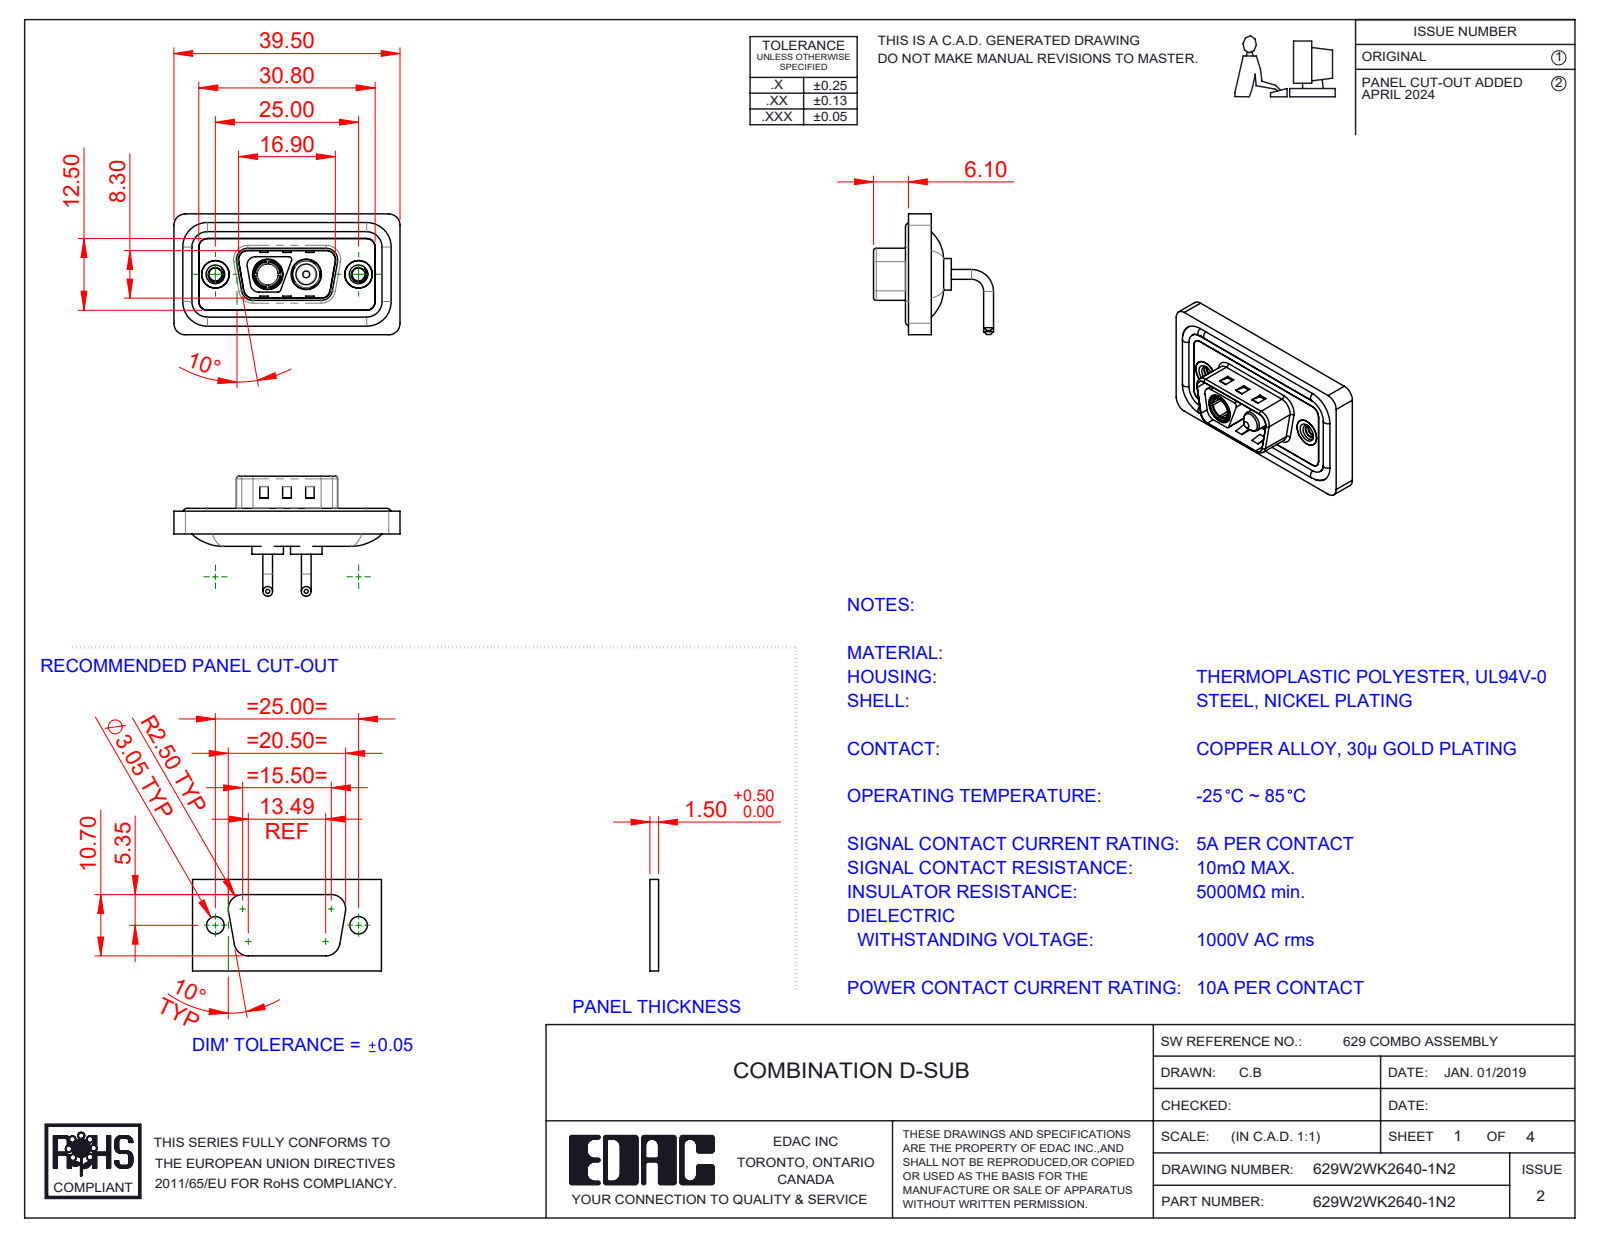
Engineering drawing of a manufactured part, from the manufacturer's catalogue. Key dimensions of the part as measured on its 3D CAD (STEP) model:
Part name (STEP PRODUCT): Power Socket_10A RA; 629Combo Waterproof Housing_09 Contacts; 629Combo Threaded Rivet_2; 629Combo Shell Rear_09 Contacts (+4 more)
STEP written by: SolidWorks 2023 (CONFIG_CONTROL_DESIGN)
Units: millimetres
Bodies: 11 solids, 542 faces (189 planar, 231 cylindrical, 122 other)
Overall size (bounding box): 39.5 × 21.1 × 20.95
Volume: 4 574 mm³ · Surface area: 7 428 mm²
Round holes (diameter × count): ⌀2.26 ×2, ⌀4 ×2, ⌀4.8 ×2, ⌀4.85 ×2, ⌀5 ×2, ⌀5.3 ×2, ⌀3.7 ×1
Round bosses / shafts (diameter × count): ⌀1.7 ×4, ⌀1.6 ×4, ⌀5.5 ×2, ⌀5.2 ×2, ⌀4.9 ×2, ⌀4.75 ×2, ⌀3.75 ×2, ⌀4.96 ×1
Partial cylindrical surfaces — rounded edges, fillets, slot ends (radius × count): R1.5 ×20, R2 ×18, R0.5 ×10, R1.6 ×8, R0.25 ×4, R0.6 ×4, R0.65 ×4, R0.9 ×4
Main face-to-face distances: 0.4, 2.9, 1.1, 0.8, 2.1, 2.5, 3.1, 1.6, 4.5, 1.5
Hole centre spacings: 9.14, 15.86, 6.72, 25
